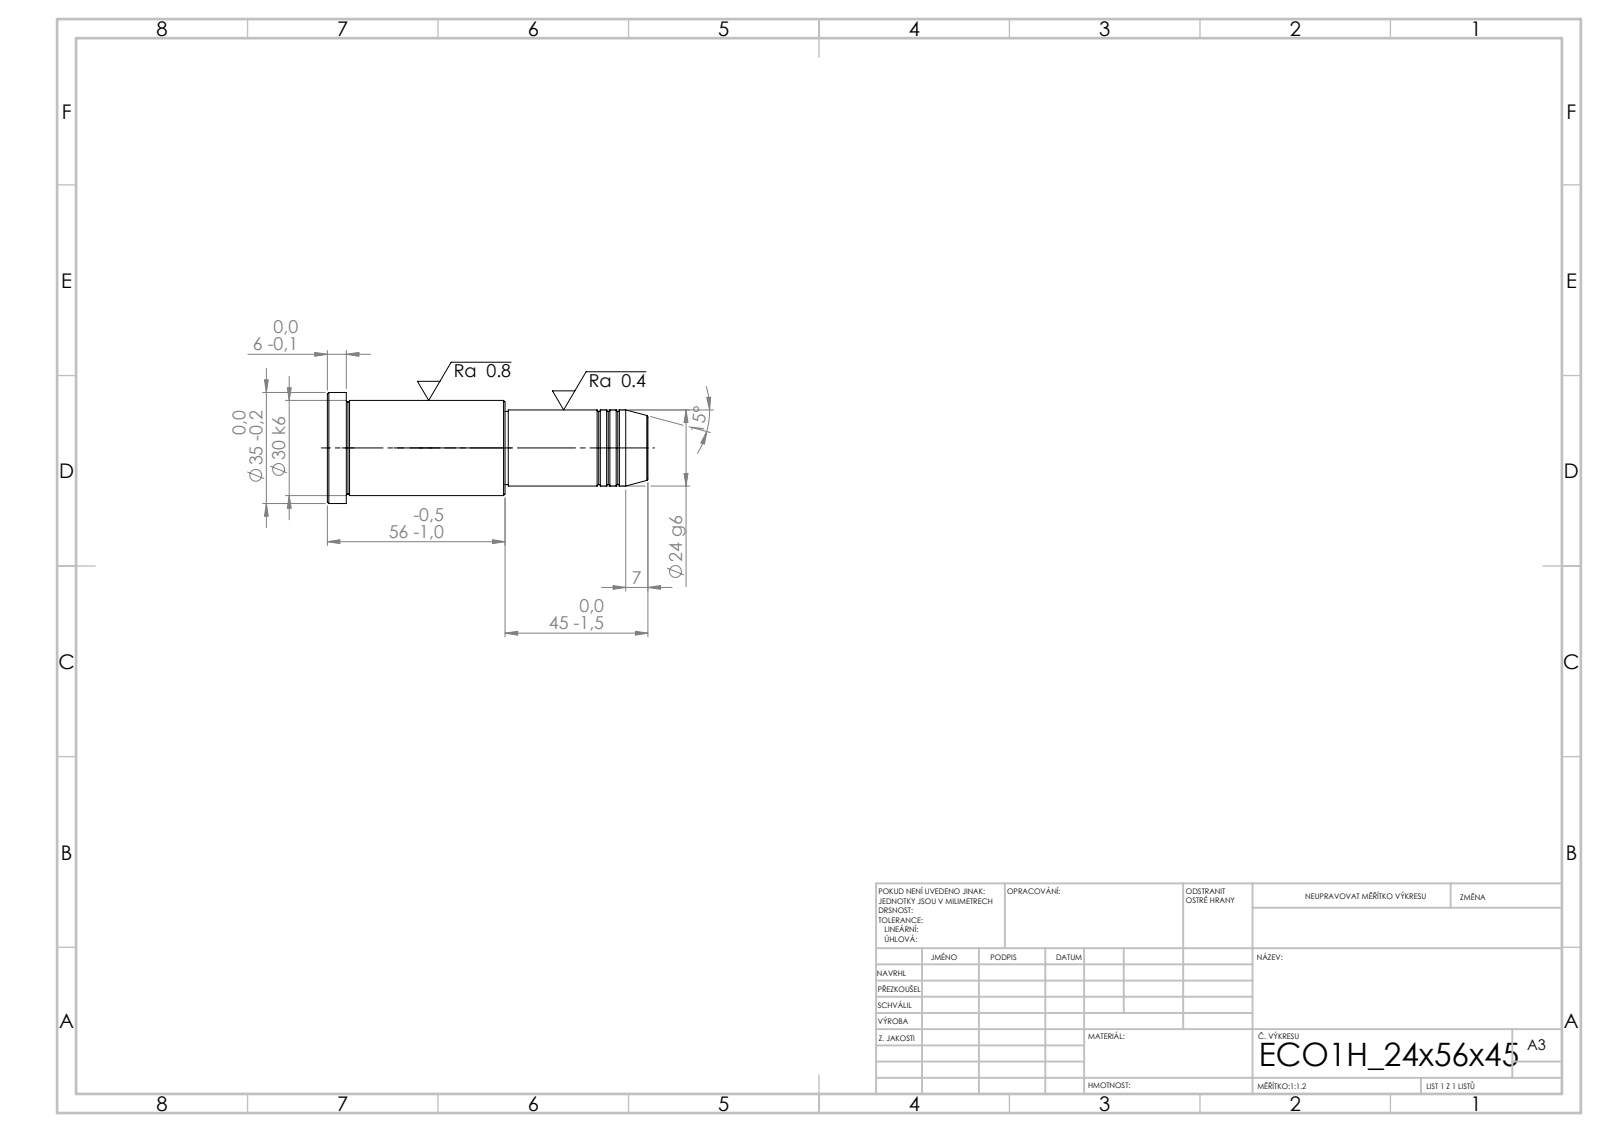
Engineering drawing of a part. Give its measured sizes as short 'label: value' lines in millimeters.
written by: SolidWorks 2019 (CONFIG_CONTROL_DESIGN)
unit: mm
bodies: 1 solid, 43 faces (5 planar, 14 cylindrical, 24 other)
size: 101 × 35 × 35
volume: 60 816 mm³; area: 10 708 mm²
bosses: 1× ⌀35, 1× ⌀30, 1× ⌀24, 1× ⌀23
face distances: 101, 95, 6, 45, 50, 56, 44, 1, 51, 57
